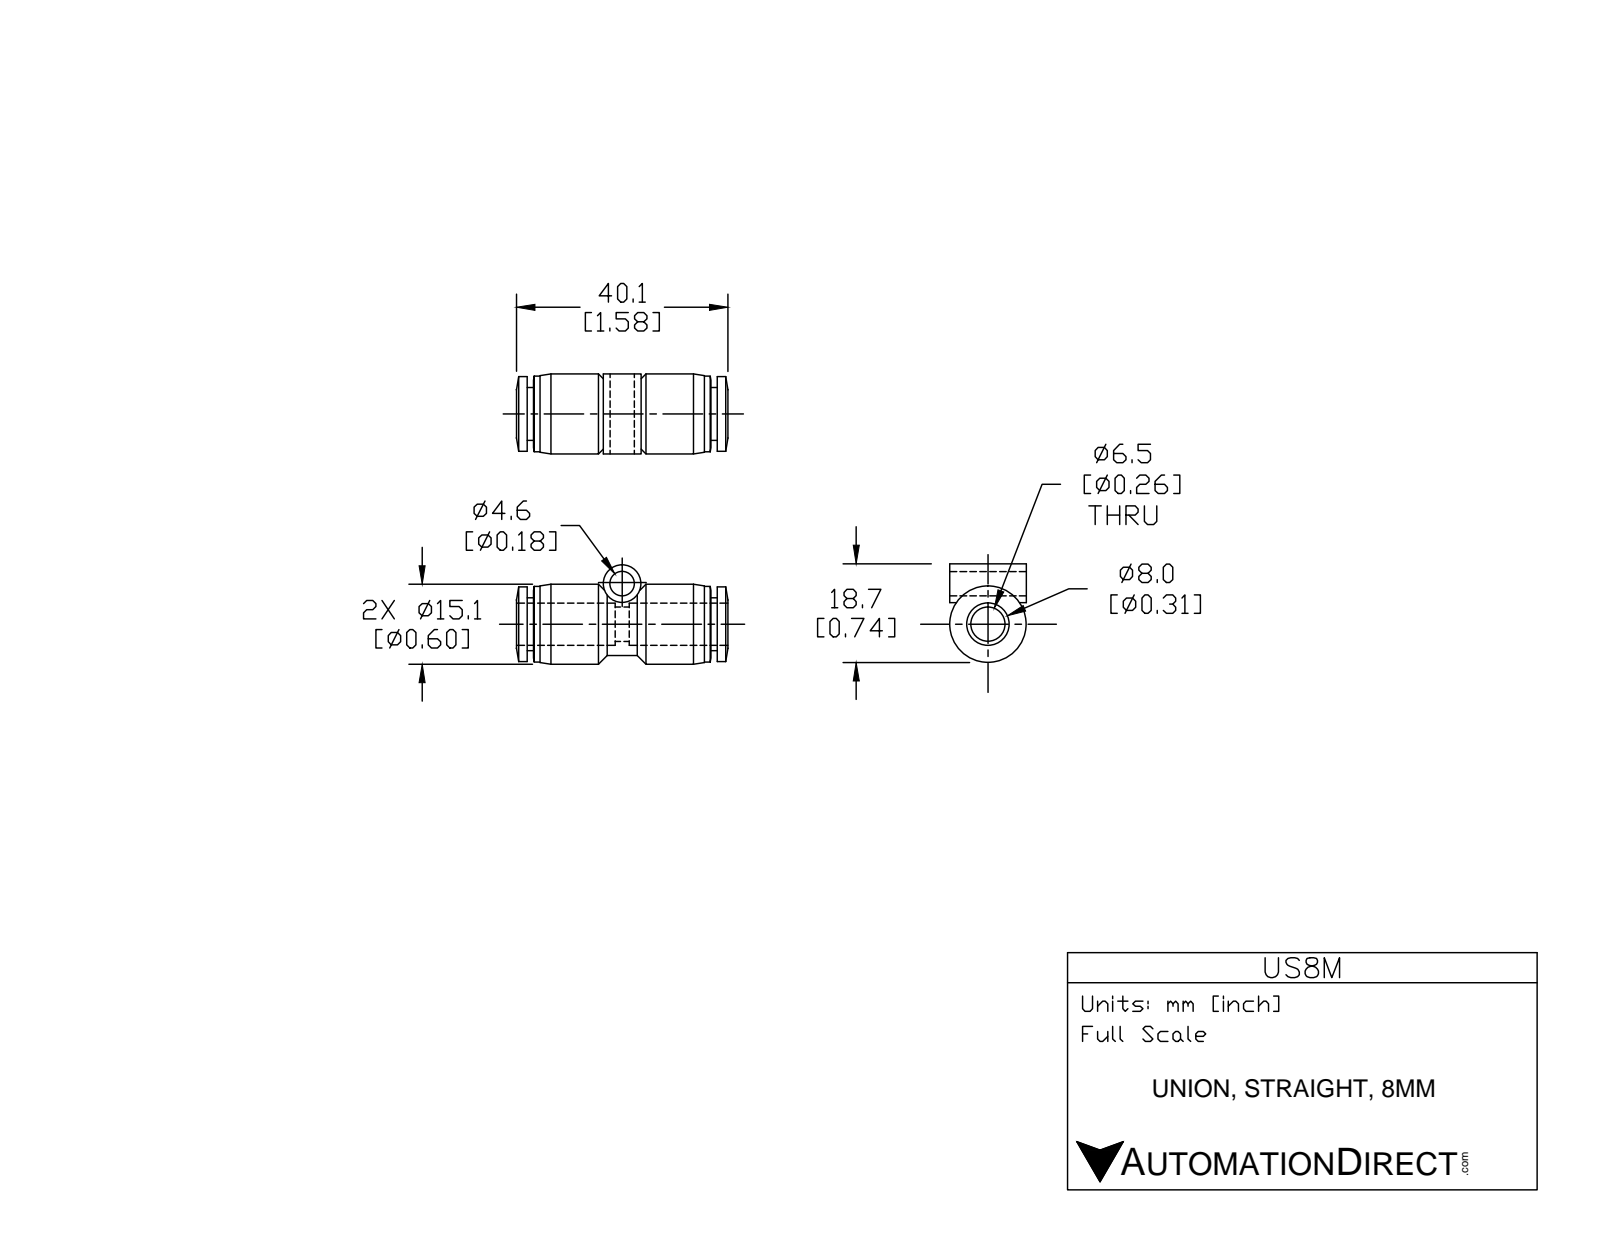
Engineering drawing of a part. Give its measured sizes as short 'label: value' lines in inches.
name: US8M
written by: SolidWorks 2015 (AUTOMOTIVE_DESIGN)
unit: in
bodies: 1 solid, 61 faces (12 planar, 29 cylindrical, 20 other)
size: 1.543 × 0.724 × 0.583
volume: 0.247 in³; area: 5.759 in²
holes: 1× ⌀0.177, 1× ⌀0.268, 1× ⌀0.327
bosses: 1× ⌀0.583, 1× ⌀0.551, 1× ⌀0.543, 1× ⌀0.457, 1× ⌀0.386, 1× ⌀0.276
face distances: 0.045, 1.341, 1.386, 1.295, 0.642, 0.744, 0.596, 0.699, 0.571, 0.102
